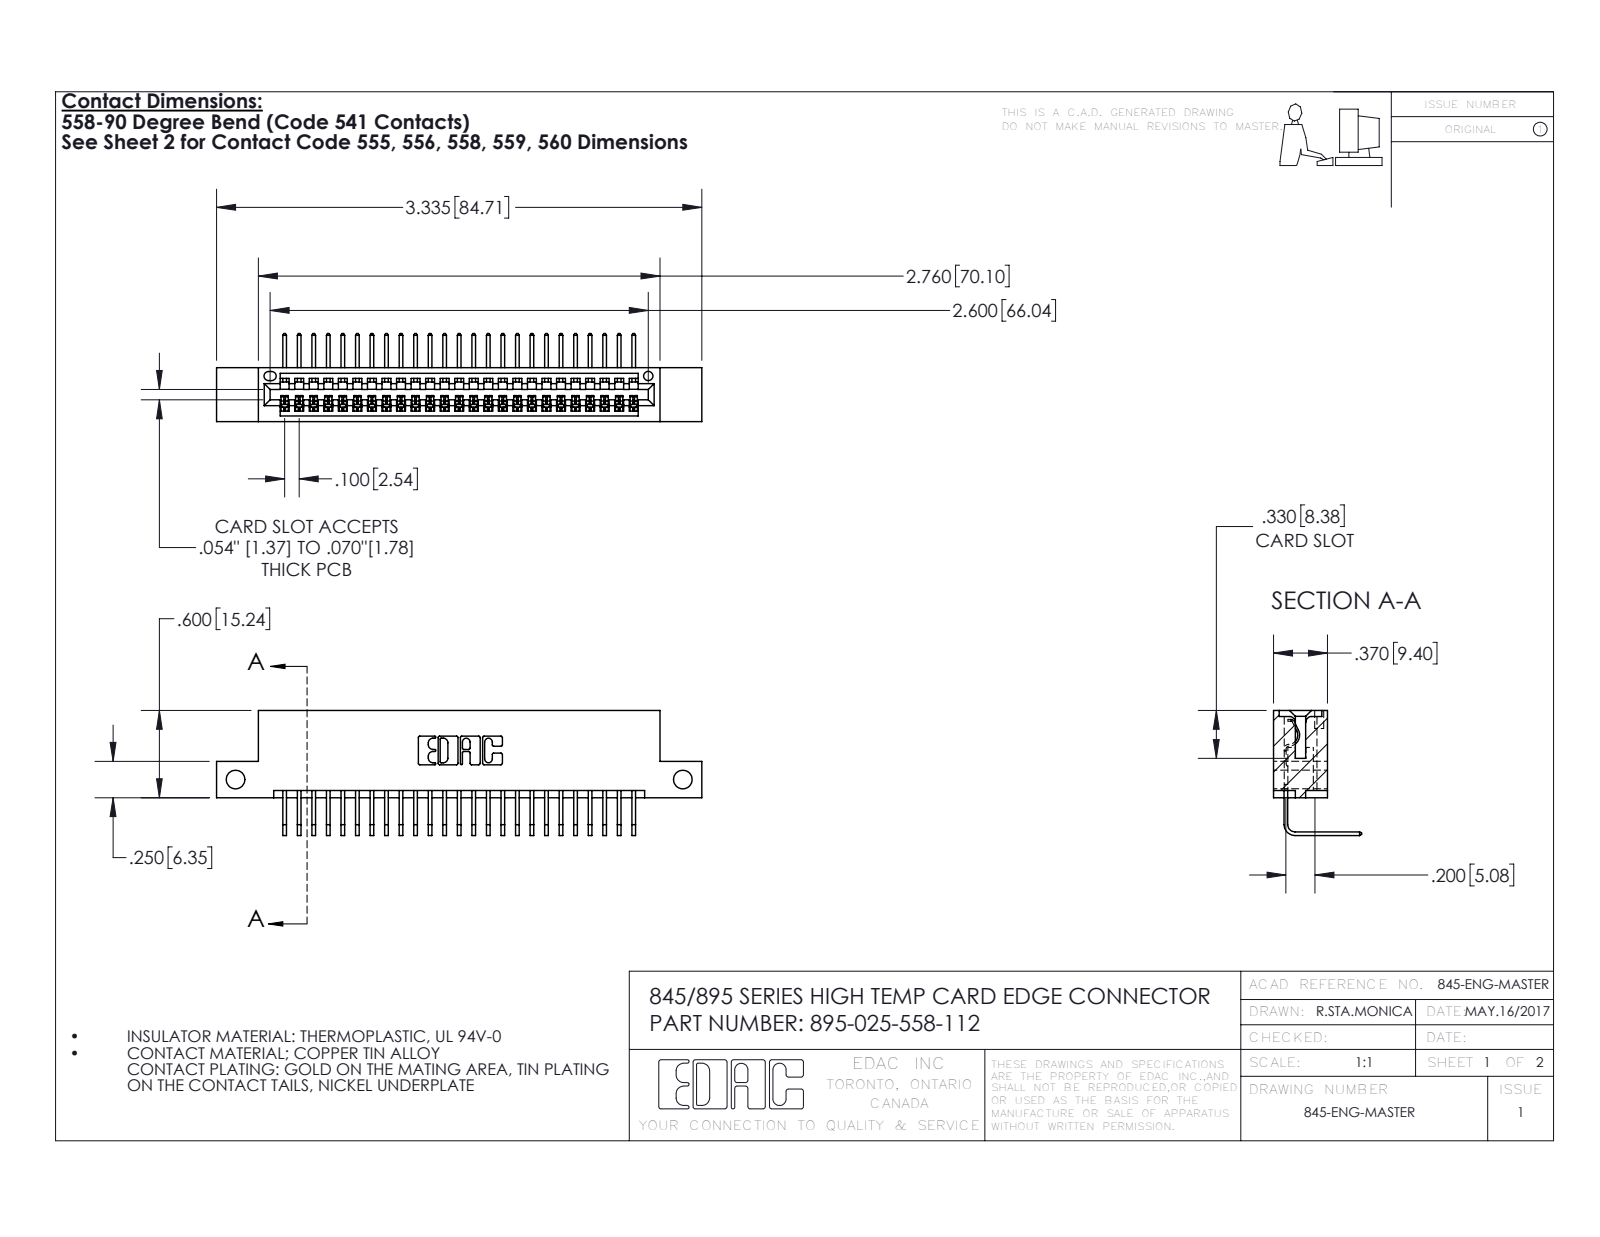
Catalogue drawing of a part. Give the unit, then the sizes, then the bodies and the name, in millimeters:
Units: millimetres
Overall size (bounding box): 84.7 × 21.8 × 15.4
Round holes (diameter × count): ⌀3.3 ×2, ⌀1.6 ×1
Partial cylindrical surfaces — rounded edges, fillets, slot ends (radius × count): R0.2 ×50, R0.3 ×22, R0.2 ×6, R0.8 ×6, R0.7 ×3, R0.8 ×2, R1 ×2, R0.4 ×1
Main face-to-face distances: 7.6, 1.8, 5.1, 9.4, 2.5, 6.9, 0.6, 5.7, 3.8, 1.8
Hole centre spacings: 78.1
Volume: 7 900 mm³ · Surface area: 10 620 mm²
Bodies: 26 solids, 1626 faces (1130 planar, 496 cylindrical, 0 other)
Part name (STEP PRODUCT): 345 Part_Flush Mounting Lugs - Side Mount; 345-292-001_558 Tail - 2; 395-025-558-112
STEP written by: SolidWorks 2016 (CONFIG_CONTROL_DESIGN)
